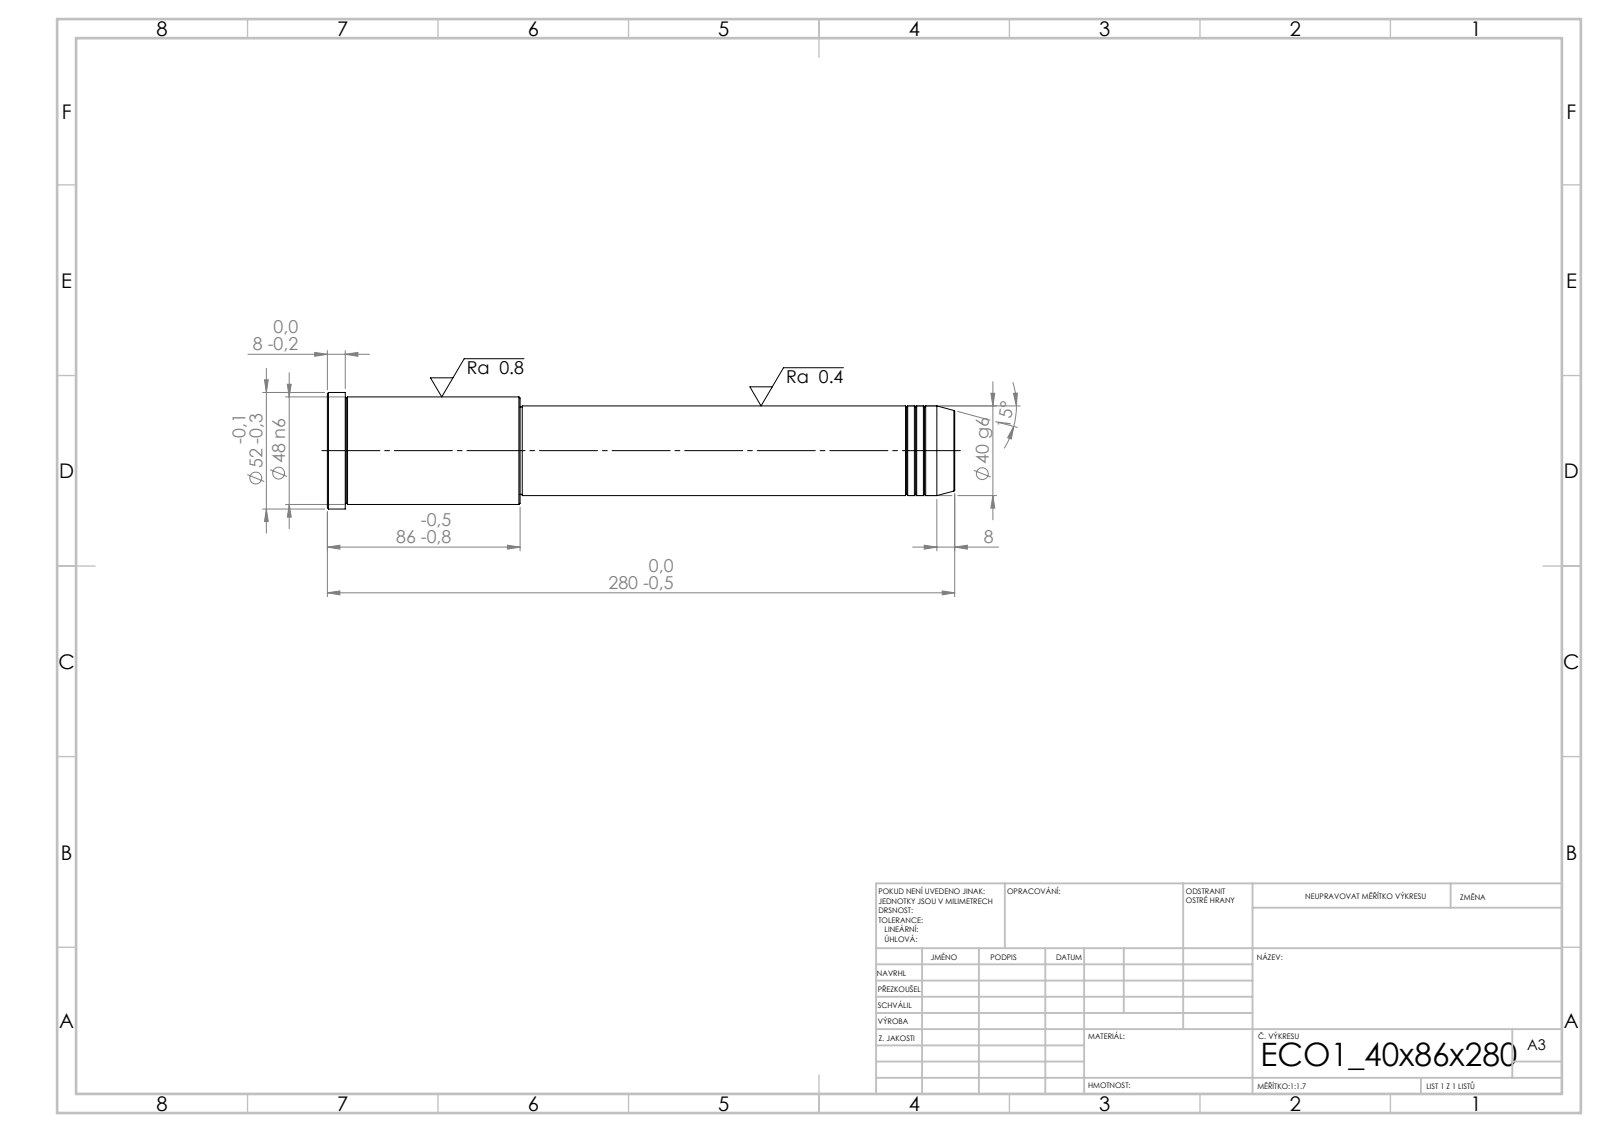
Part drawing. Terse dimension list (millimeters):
written by: SolidWorks 2019 (CONFIG_CONTROL_DESIGN)
unit: mm
bodies: 1 solid, 43 faces (5 planar, 14 cylindrical, 24 other)
size: 280 × 52 × 52
volume: 400 574 mm³; area: 41 724 mm²
bosses: 1× ⌀52, 1× ⌀48, 1× ⌀40, 1× ⌀39
face distances: 280, 194, 86, 272, 78, 8, 193, 1, 79, 87
